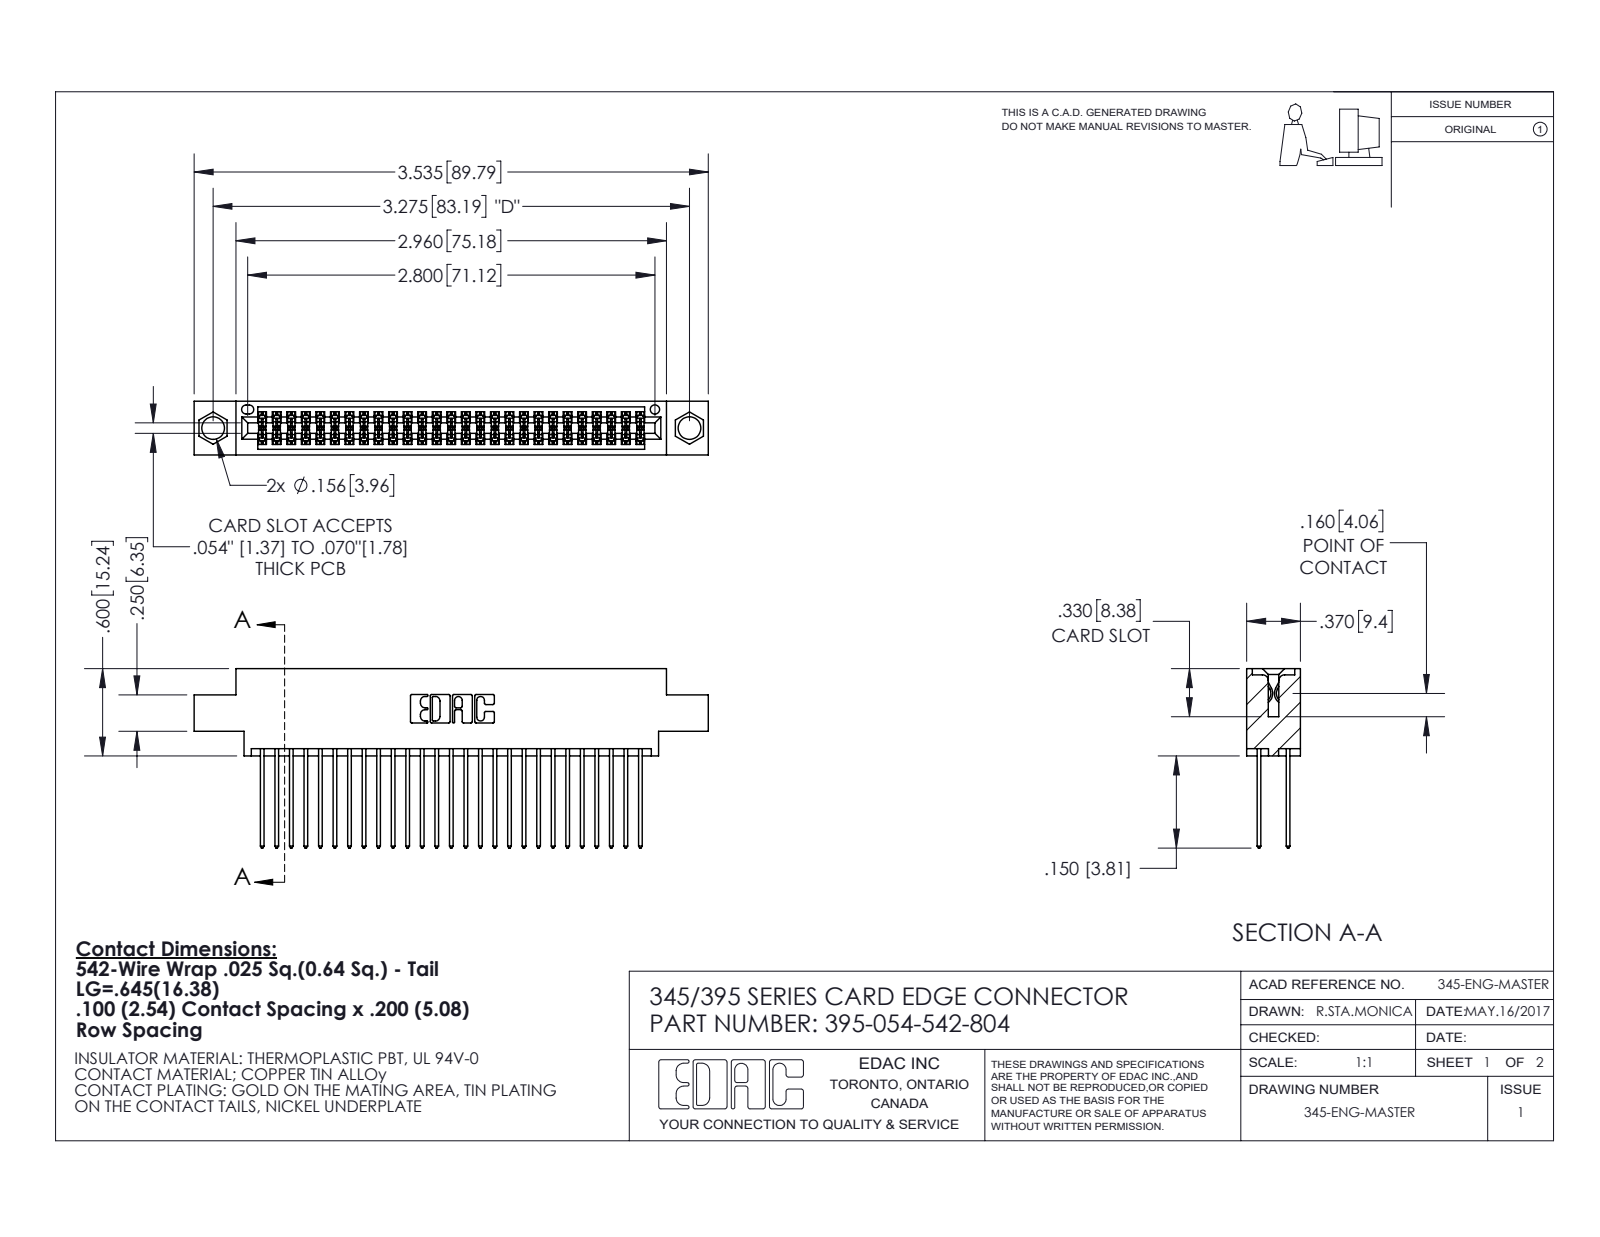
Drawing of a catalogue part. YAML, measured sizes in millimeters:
part_name: "345 Part_0.170 Offset - 0.156 Dia-TI; 345-292-001_345-293-142; 395-054-542-804"
step_written_by: "SolidWorks 2020 (CONFIG_CONTROL_DESIGN)"
units: millimeters
bodies: {solids: 55, faces: 2844, planar: 1880, cylindrical: 964, other: 0}
overall_size: [89.8, 31.3, 9.4]
volume: 8620
surface_area: 13610
round_holes:
  - {diameter: 4, count: 2}
  - {diameter: 1.6, count: 1}
partial_cylinders:
  - {radius: 0.2, count: 108}
  - {radius: 0.3, count: 54}
  - {radius: 0.3, count: 22}
  - {radius: 0.2, count: 6}
  - {radius: 0.8, count: 6}
  - {radius: 0.7, count: 3}
  - {radius: 0.4, count: 2}
  - {radius: 0.5, count: 2}
face_to_face_distances: [1.8, 7.6, 5.1, 2.5, 6.9, 0.6, 9.4, 5.7, 4.4, 3.8]
hole_center_spacings: [6.9, 77.2, 83.2]
